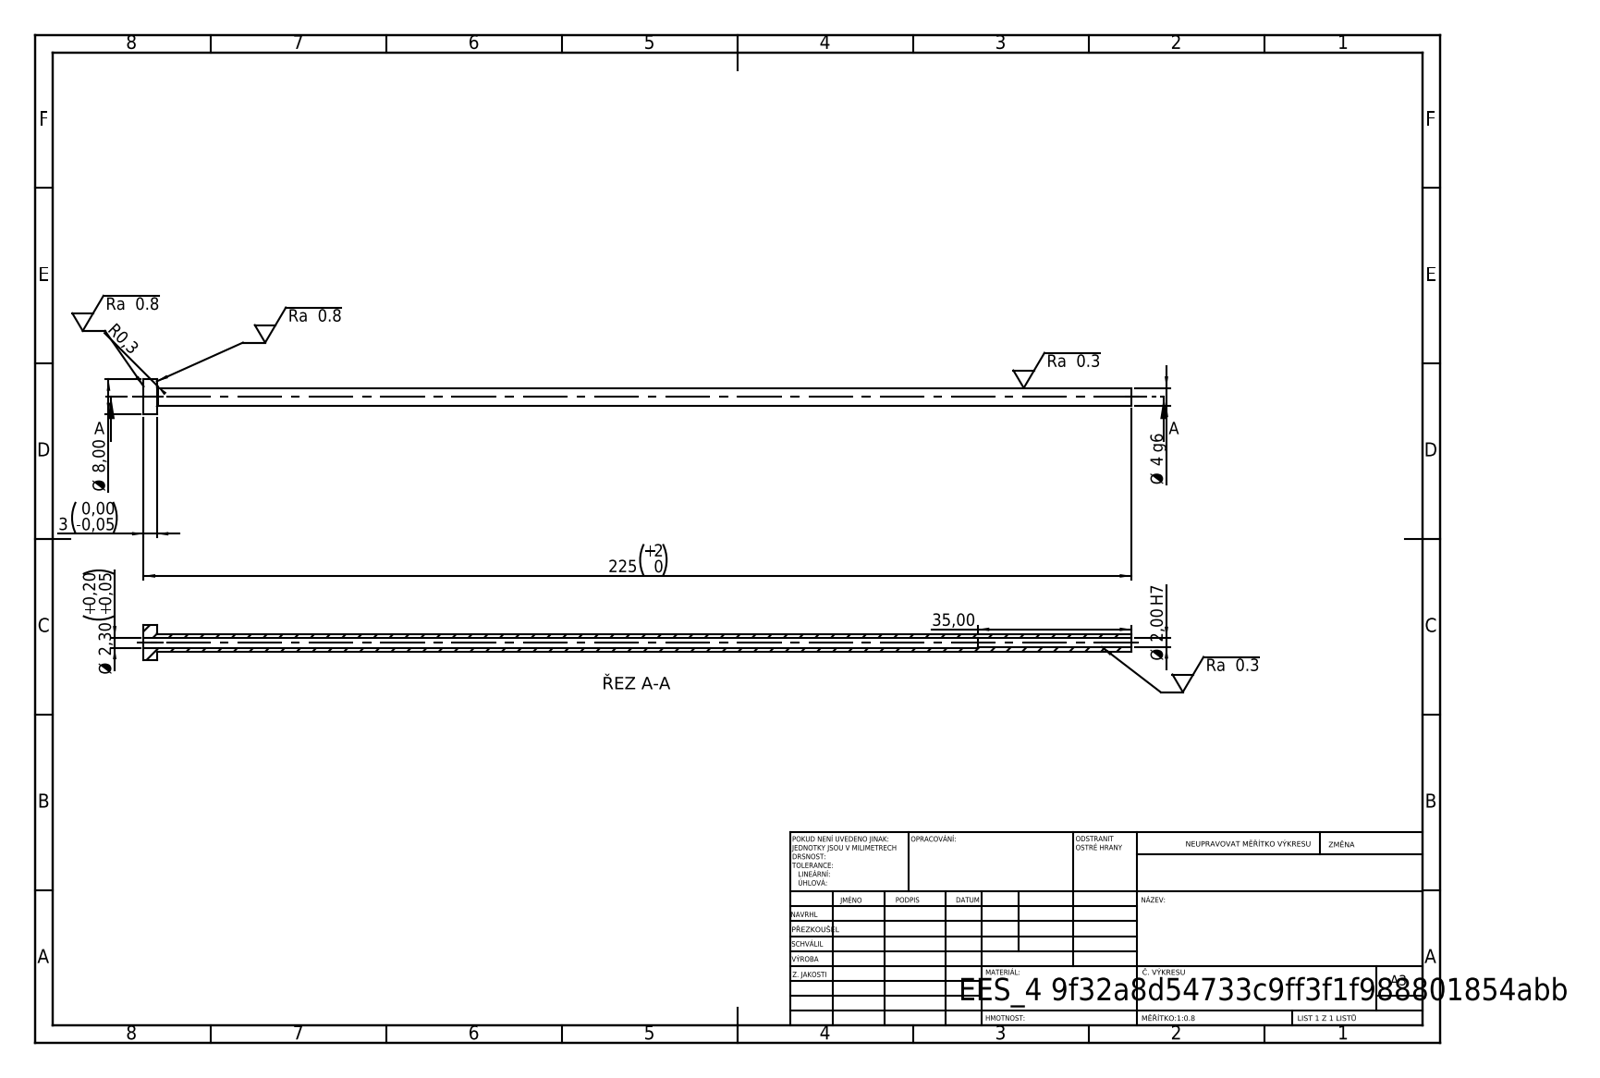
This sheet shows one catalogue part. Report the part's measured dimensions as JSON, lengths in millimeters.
{"step_written_by": "SolidWorks 2019 (CONFIG_CONTROL_DESIGN)", "units": "millimeters", "bodies": {"solids": 1, "faces": 14, "planar": 4, "cylindrical": 8, "other": 2}, "overall_size": [225, 8, 8], "volume_mm3": 2041, "surface_area_mm2": 4551, "round_holes": [[2, 1], [2.3, 1]], "round_bosses_or_shafts": [[8, 1], [4, 1]], "face_to_face_distances": [3, 225, 222, 190, 187, 35]}
